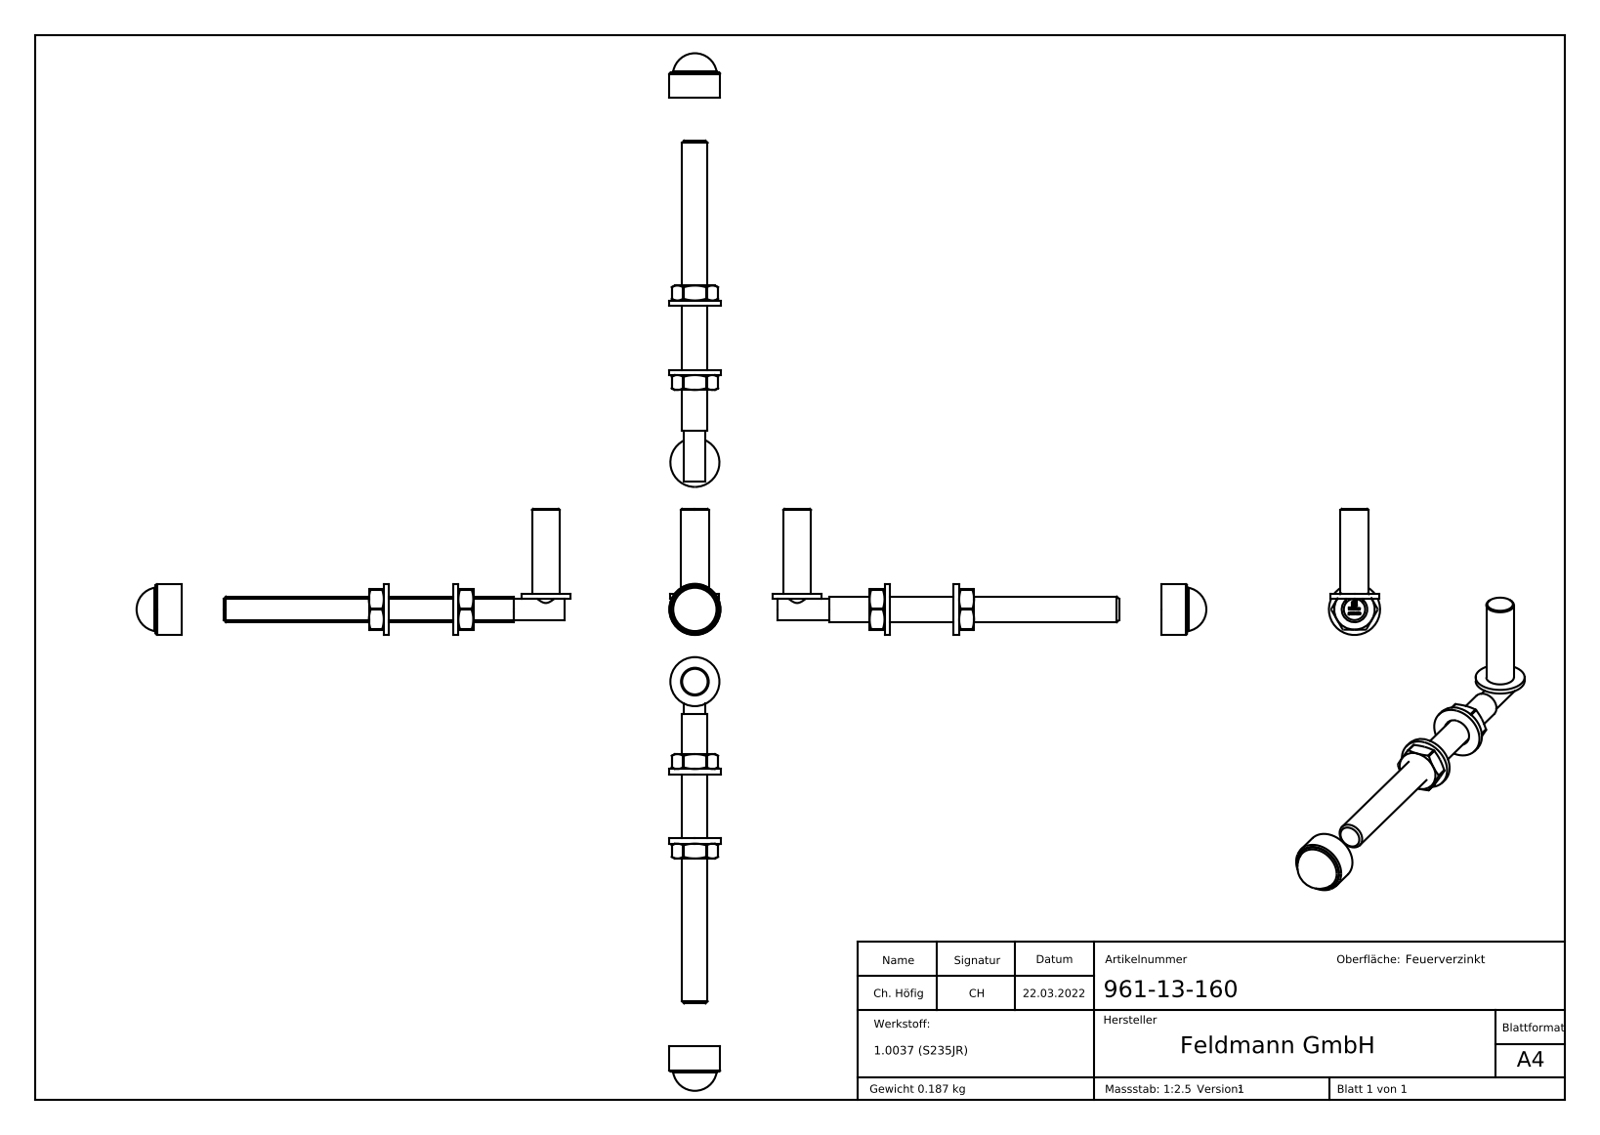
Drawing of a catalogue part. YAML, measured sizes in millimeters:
part_name: "961-13-160; 961-1X-XXX Teil1_961-13-160 Teil1; DIN 125 M4-M20_DIN 125 M12; 961-1X-XXX Teil2_961-XX-XXX Teil2 (+1 more)"
step_written_by: "SolidWorks 2018 (CONFIG_CONTROL_DESIGN)"
units: millimeters
bodies: {solids: 6, faces: 357, planar: 180, cylindrical: 25, other: 152}
overall_size: [203.5, 59.2, 24]
volume: 30235
surface_area: 15665
round_holes:
  - {diameter: 10.2, count: 1}
  - {diameter: 13, count: 1}
  - {diameter: 19, count: 1}
round_bosses_or_shafts:
  - {diameter: 24, count: 1}
  - {diameter: 23.8, count: 1}
  - {diameter: 23, count: 1}
  - {diameter: 13, count: 1}
  - {diameter: 12, count: 1}
  - {diameter: 10, count: 1}
  - {diameter: 8, count: 1}
partial_cylinders:
  - {radius: 0.5, count: 6}
face_to_face_distances: [19, 2.5, 32.5, 35, 42, 9.5, 7, 39.5, 30, 2]
